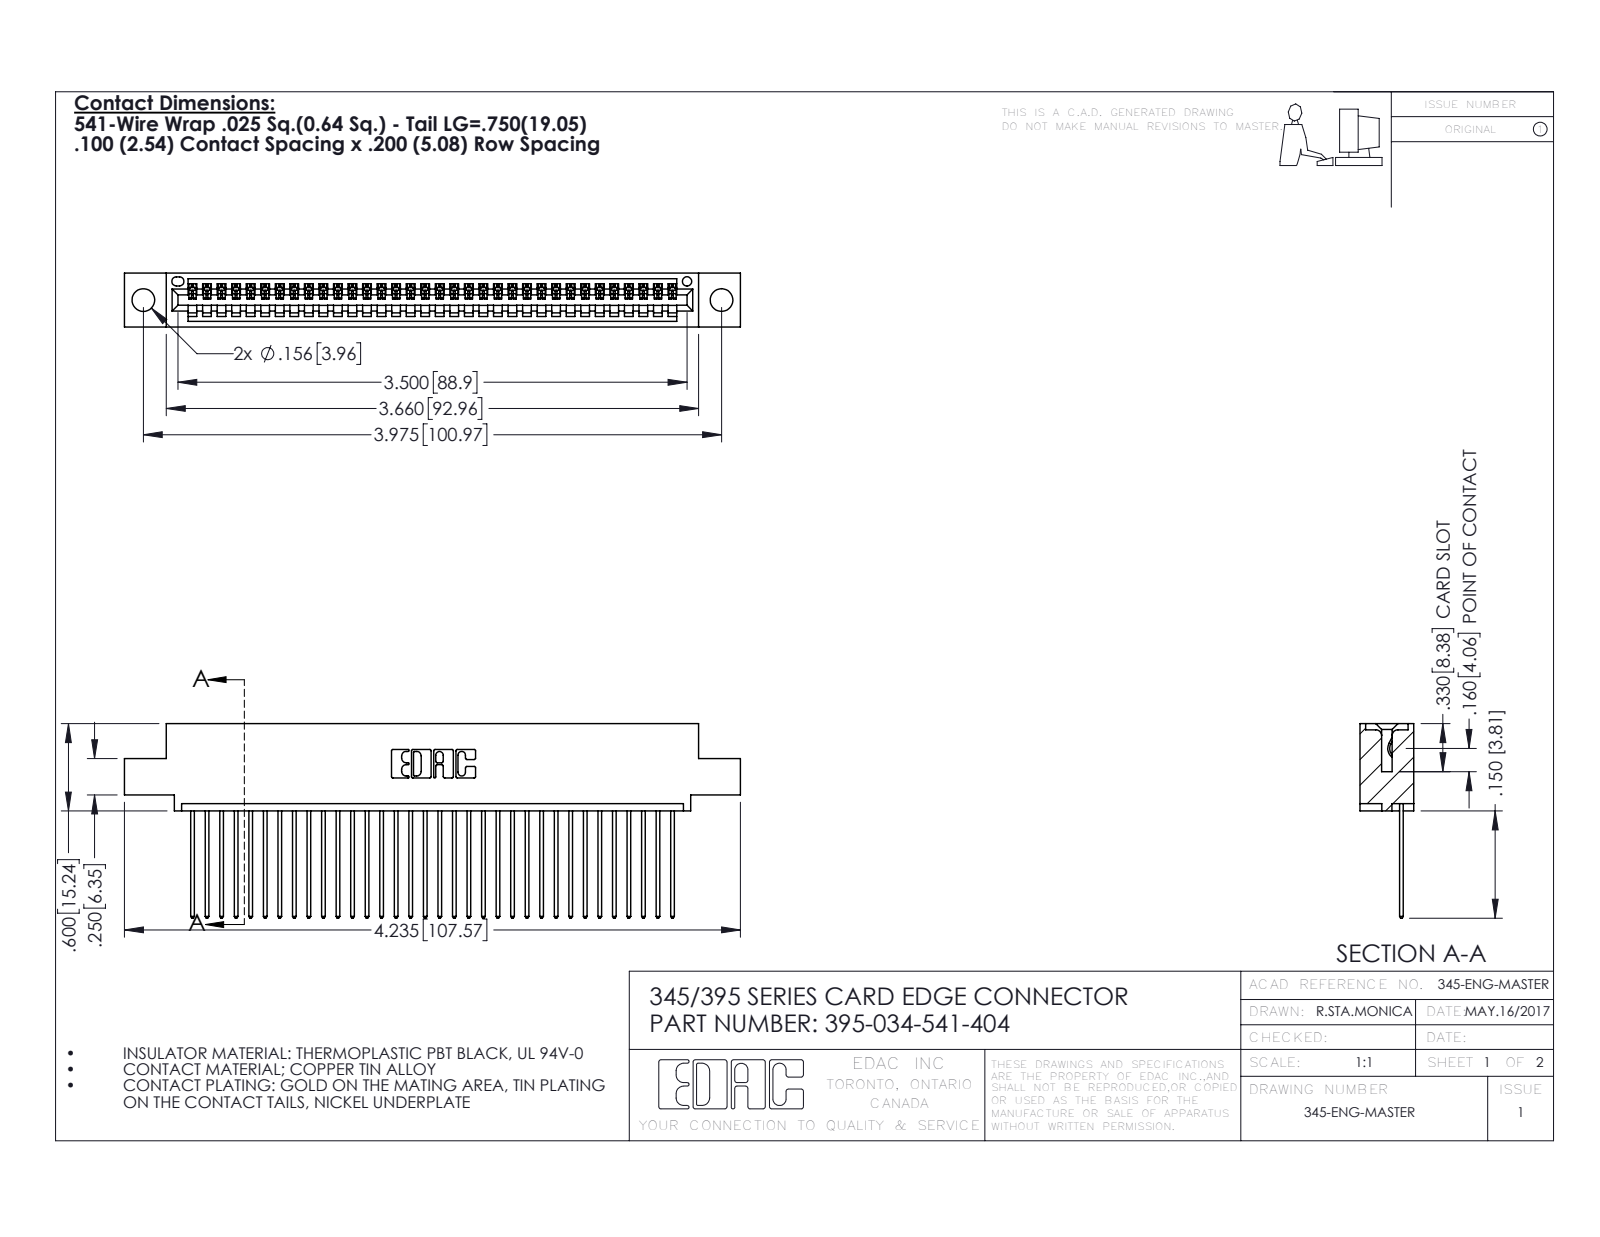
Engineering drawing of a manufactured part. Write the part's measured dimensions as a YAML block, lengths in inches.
part_name: "345 Part_0.110 Offset - 0.156 Dia-TH; 395-034-541-404; 345-292-001_345-293-141"
step_written_by: "SolidWorks 2016 (CONFIG_CONTROL_DESIGN)"
units: inches
bodies: {solids: 35, faces: 2102, planar: 1444, cylindrical: 658, other: 0}
overall_size: [4.235, 1.337, 0.37]
volume: 0.616
surface_area: 21.49
round_holes:
  - {diameter: 0.156, count: 2}
  - {diameter: 0.064, count: 1}
partial_cylinders:
  - {radius: 0.006, count: 68}
  - {radius: 0.01, count: 68}
  - {radius: 0.01, count: 22}
  - {radius: 0.007, count: 6}
  - {radius: 0.031, count: 6}
  - {radius: 0.026, count: 3}
  - {radius: 0.031, count: 2}
  - {radius: 0.04, count: 2}
face_to_face_distances: [0.072, 0.298, 0.098, 0.272, 0.025, 0.37, 0.2, 0.225, 0.149, 0.072]
hole_center_spacings: [0.27, 3.74, 3.975]
